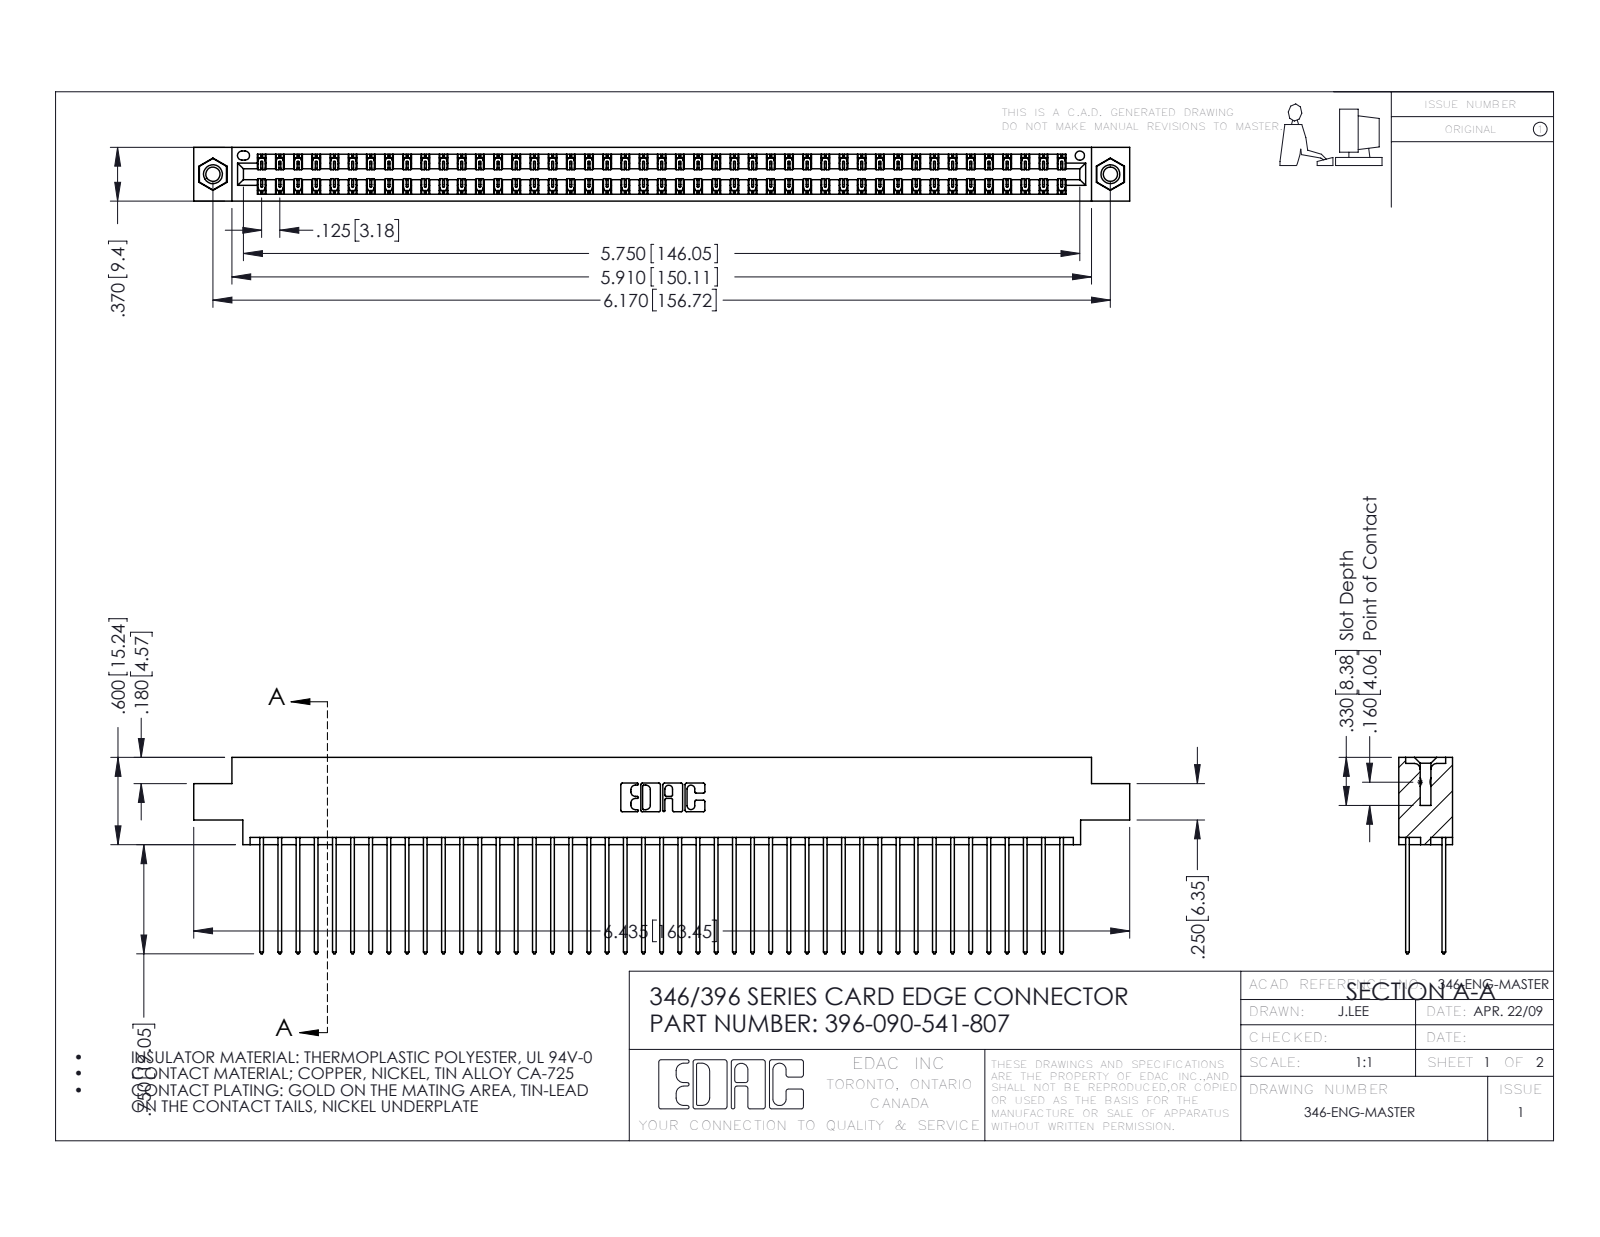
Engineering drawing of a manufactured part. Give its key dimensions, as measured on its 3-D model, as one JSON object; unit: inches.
{"part_name": "345-292-001_345-293-141; 346 Part_0.170 Offset - 0.156 Dia-TI; 345-250-001_345-250-005-103; 396-090-541-807", "step_written_by": "SolidWorks 2016 (CONFIG_CONTROL_DESIGN)", "units": "inches", "bodies": {"solids": 93, "faces": 4866, "planar": 3262, "cylindrical": 1588, "other": 16}, "overall_size": [6.435, 1.35, 0.37], "volume_in3": 0.995, "surface_area_in2": 38.99, "round_holes": [[0.098, 2], [0.125, 2], [0.156, 2], [0.064, 1]], "round_bosses_or_shafts": [[0.155, 2]], "partial_cylinders_radius": [[0.006, 135], [0.01, 90], [0.01, 22], [0.007, 6], [0.031, 6], [0.026, 3], [0.014, 2], [0.022, 2]], "face_to_face_distances": [0.048, 0.322, 0.25, 0.072, 0.298, 0.025, 0.37, 0.275, 0.225, 0.222], "hole_center_spacings": [0.246, 5.961, 6.17]}
